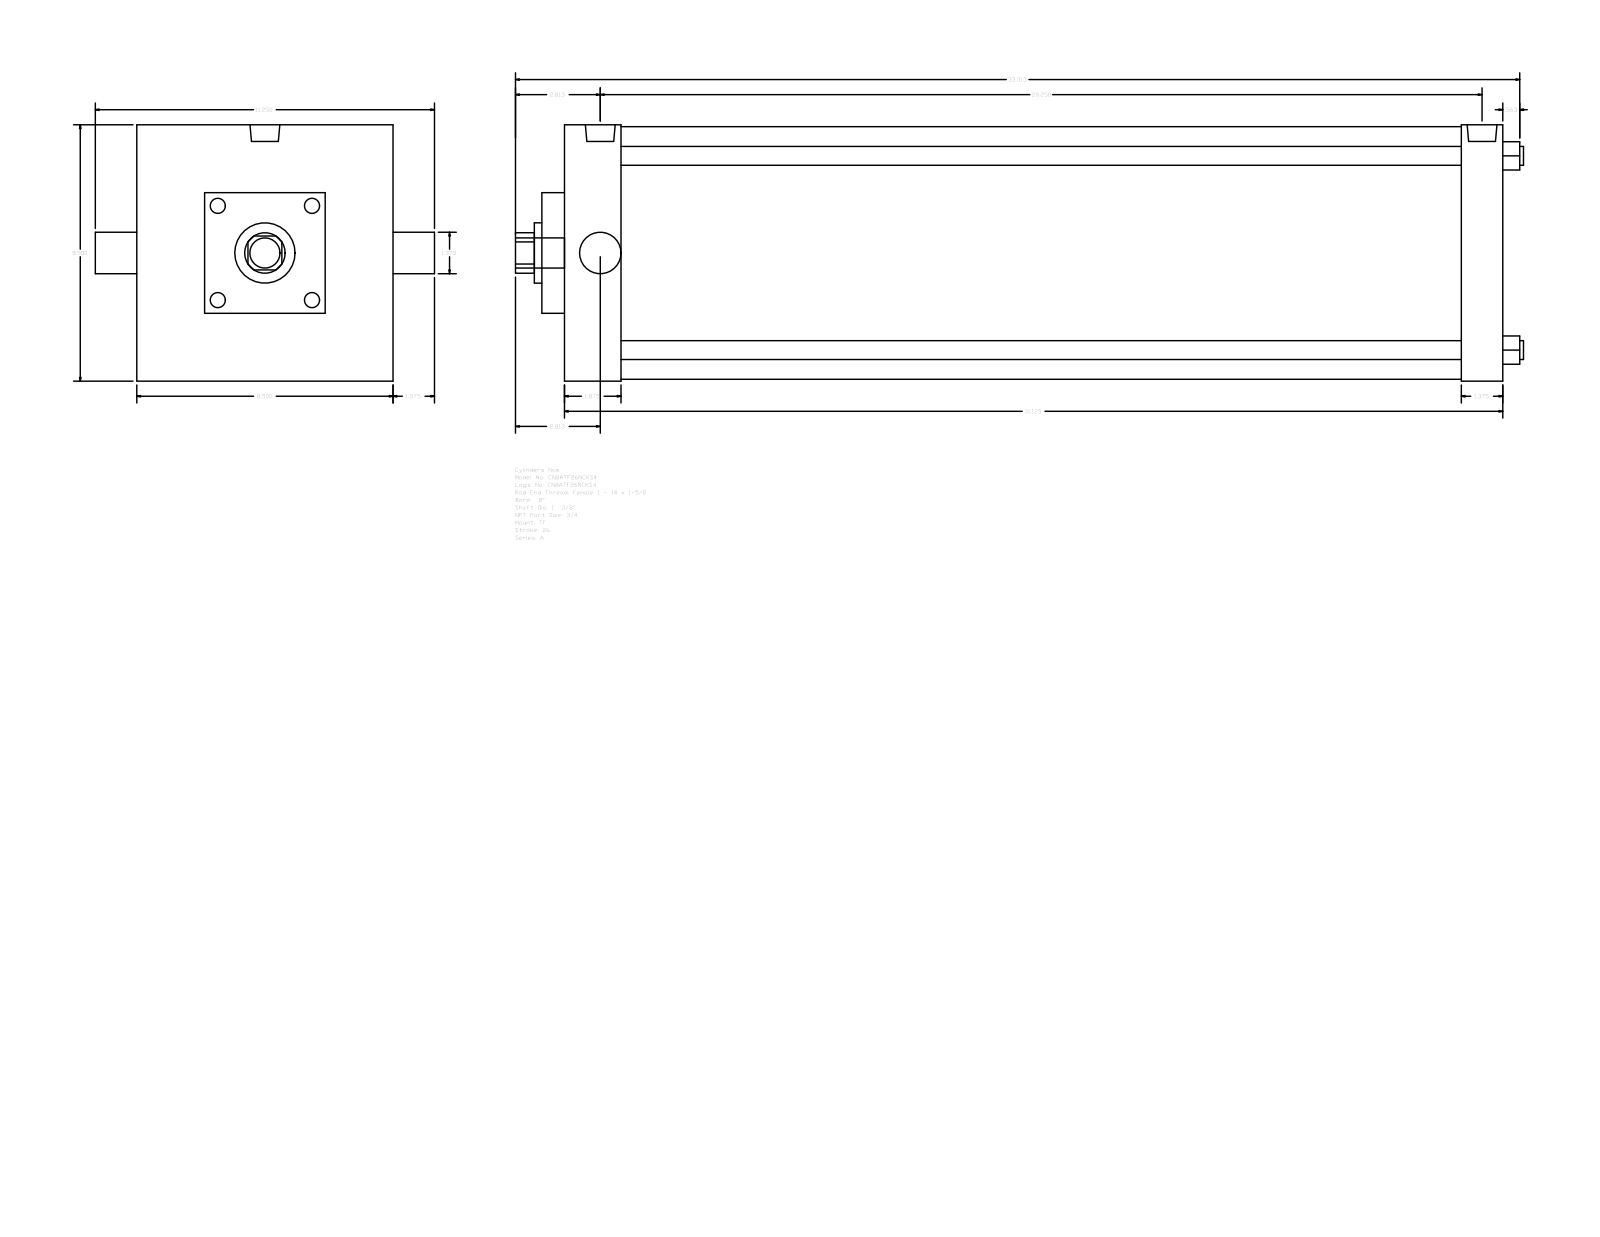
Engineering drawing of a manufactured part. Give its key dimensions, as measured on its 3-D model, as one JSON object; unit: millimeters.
{"part_name": "A_TF__0800_1.375", "step_written_by": "GSSL Pune (CONFIG_CONTROL_DESIGN)", "units": "millimeters", "bodies": {"solids": 0, "faces": 89, "planar": 65, "cylindrical": 24, "other": 0}, "overall_size": [849.31, 285.75, 215.9], "round_holes": [[15.88, 4], [34.92, 2], [50.8, 1], [212.72, 1]], "round_bosses_or_shafts": [[15.08, 3], [25.12, 2], [25.4, 1]], "partial_cylinders_radius": [[17.06, 1]], "face_to_face_distances": [790.58, 215.9, 34.93, 47.63, 742.95, 755.65, 708.02, 19.04, 66.67, 774.69], "hole_center_spacings": [115.67, 163.58, 231.34]}
